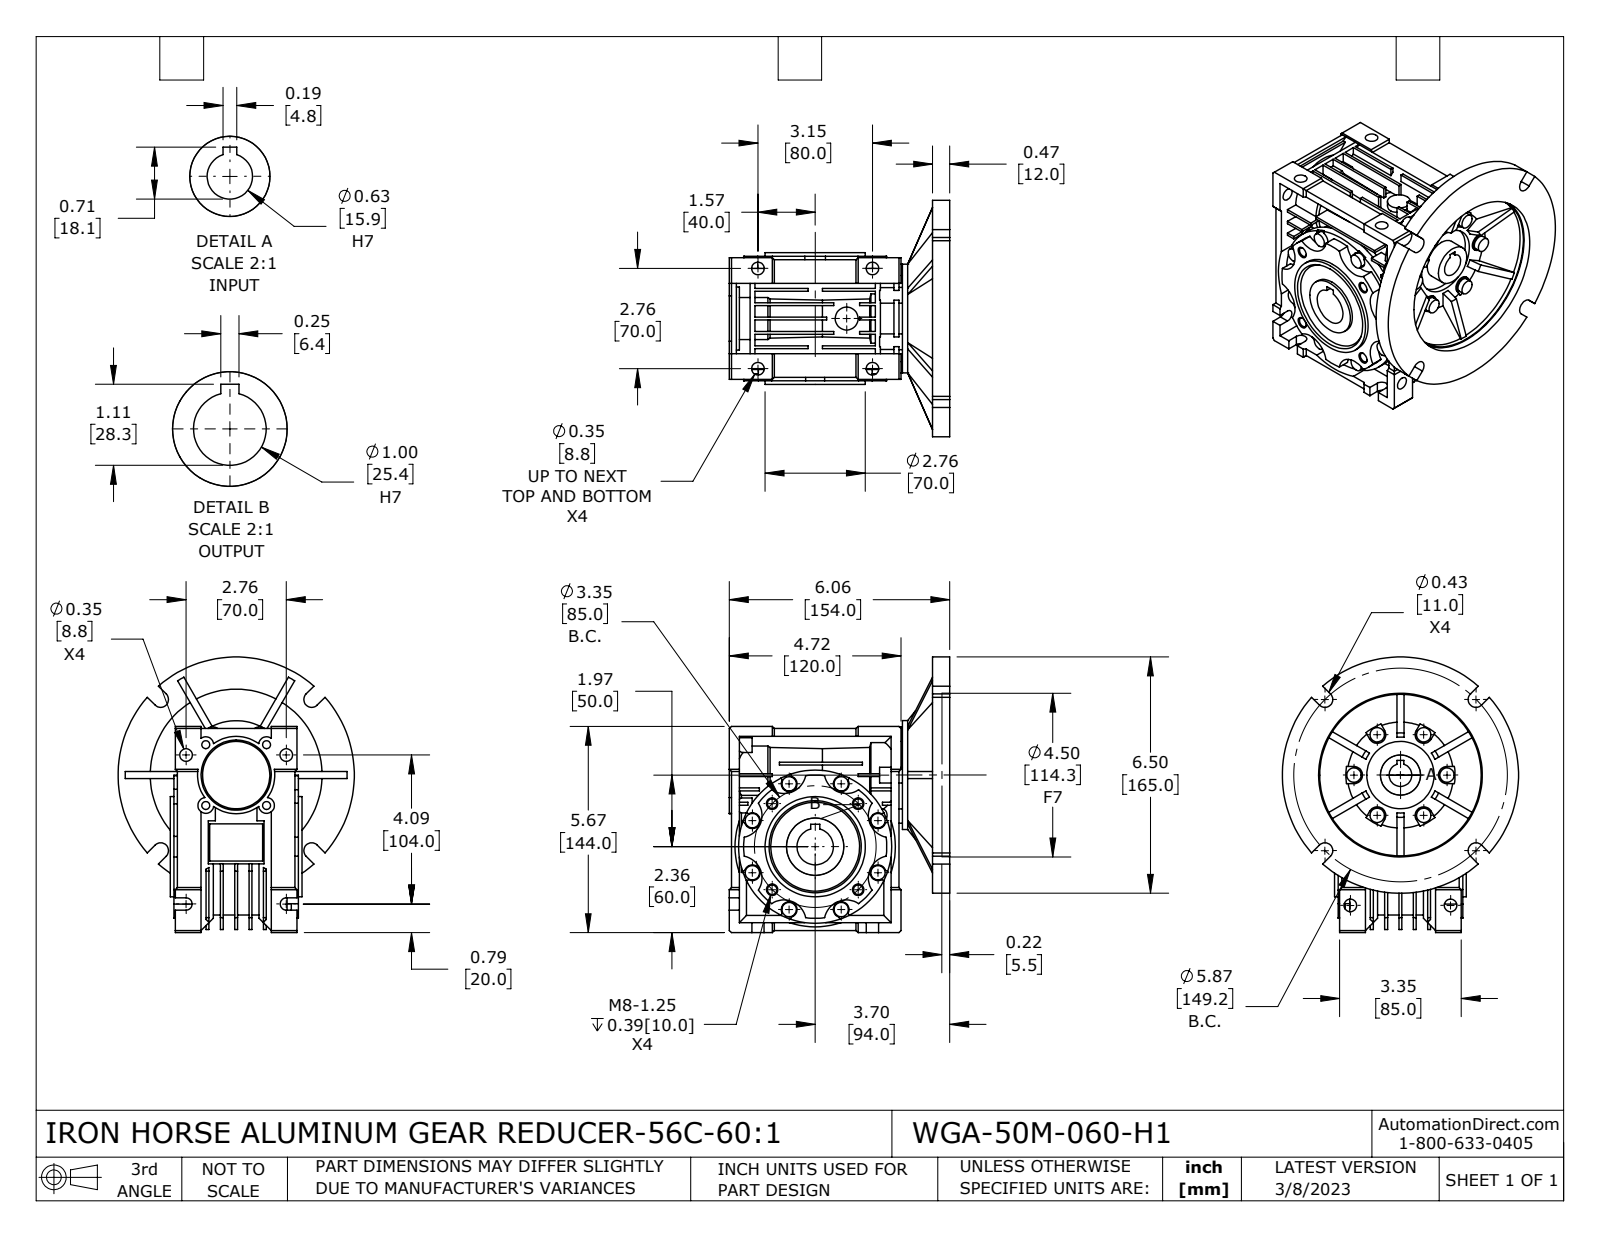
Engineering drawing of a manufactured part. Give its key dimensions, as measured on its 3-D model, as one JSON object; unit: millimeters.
{"part_name": "WGA-50M-060-H1", "step_written_by": "SolidWorks 2021 (CONFIG_CONTROL_DESIGN)", "units": "millimeters", "bodies": {"solids": 4, "faces": 954, "planar": 558, "cylindrical": 292, "other": 104}, "overall_size": [192.5, 165, 154], "volume_mm3": 1191000, "surface_area_mm2": 266100, "round_holes": [[8.8, 8], [5.6, 4], [6.7, 4], [6.7, 2], [15.9, 1], [16.5, 1], [25.4, 1], [28, 1], [34, 1], [40, 1], [47, 1], [112.8, 1]], "round_bosses_or_shafts": [[10, 14], [165, 1], [107, 1], [76, 1], [70, 1], [61, 1], [55, 1], [54, 1]], "partial_cylinders_radius": [[5.5, 22], [6, 14], [15, 8], [15.5, 8], [4.2, 6], [46, 1], [47.7, 1], [50, 1]], "face_to_face_distances": [12, 10, 2, 7, 8, 1.5, 5.5, 20, 55, 35], "hole_center_spacings": [30, 42.4, 42.5, 60.1, 70, 15.6, 37.7, 37.8]}
